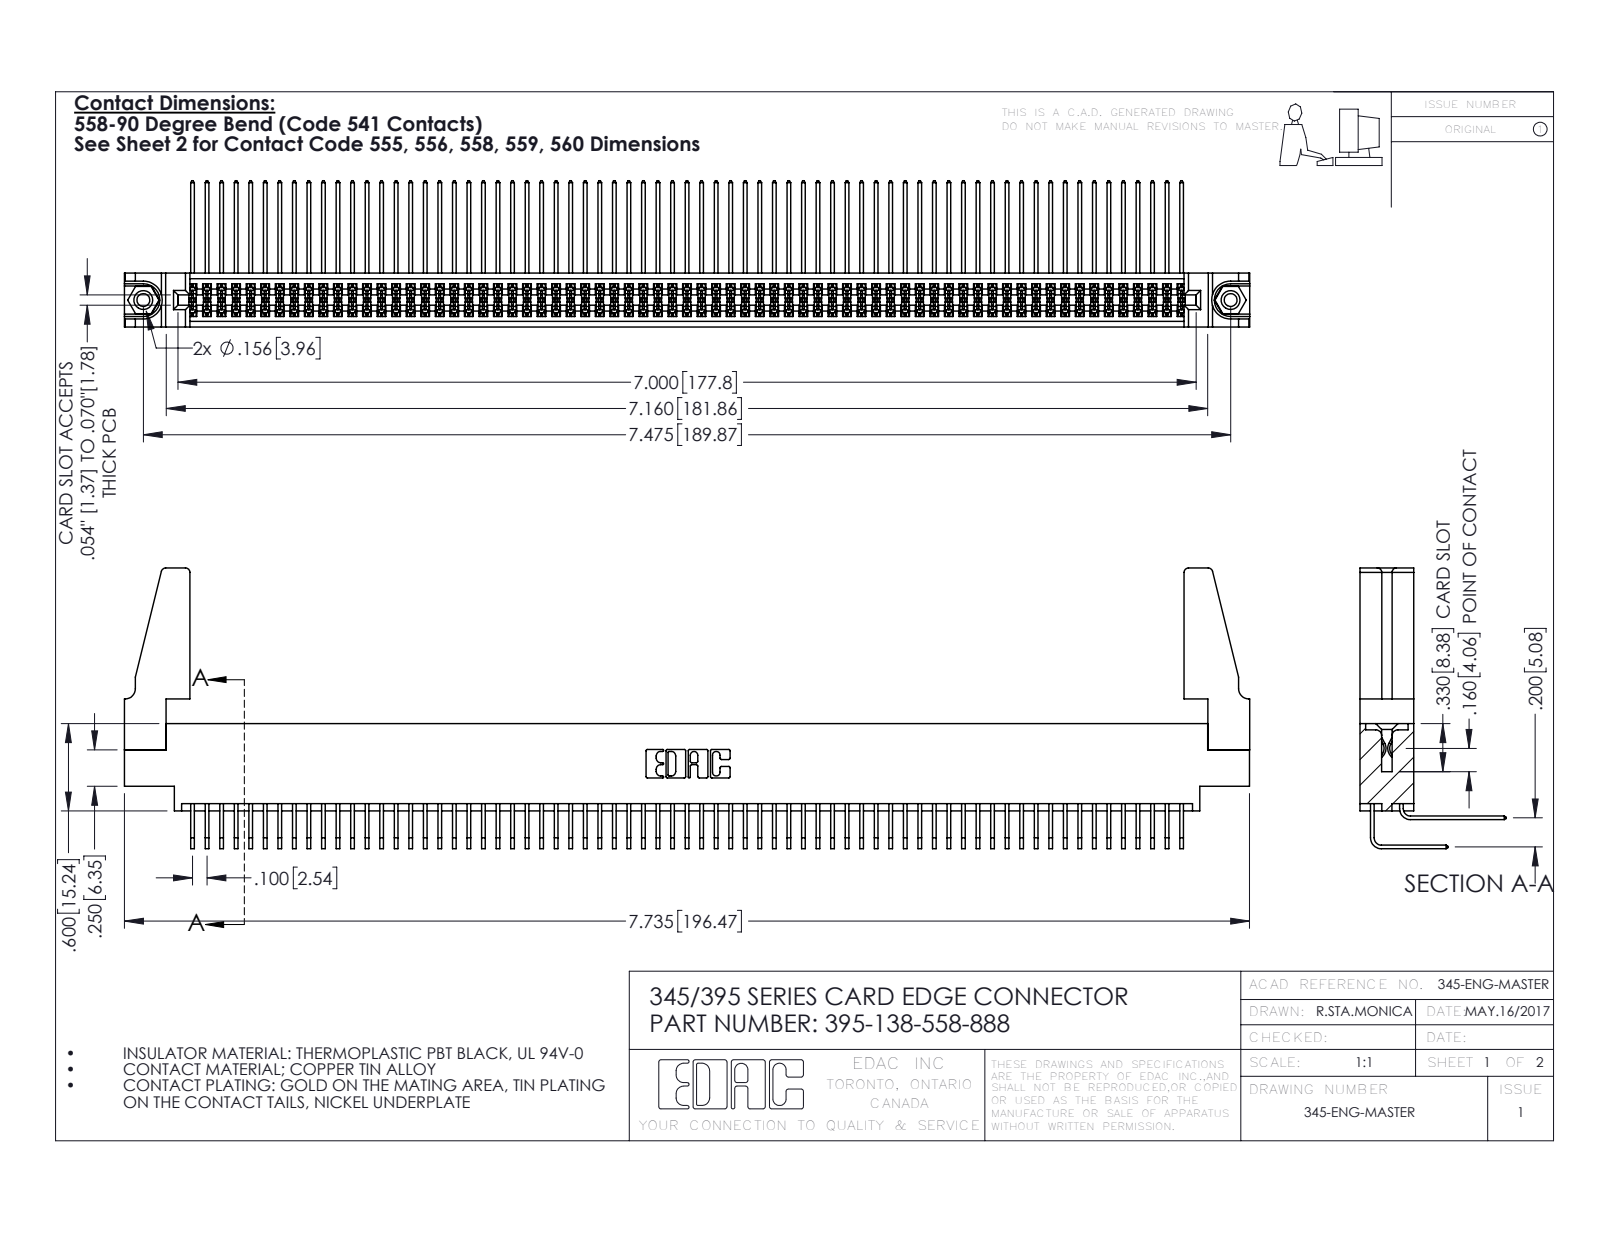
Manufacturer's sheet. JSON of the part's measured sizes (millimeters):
{"part_name": "345-292-001_558 Tail - 2; 395-138-558-888; 345-292-001_558 559 Tail - 1; 345-250-001_345-250-001-102 (+2 more)", "step_written_by": "SolidWorks 2016 (CONFIG_CONTROL_DESIGN)", "units": "millimeters", "bodies": {"solids": 143, "faces": 7430, "planar": 4986, "cylindrical": 2428, "other": 16}, "overall_size": [196.5, 49, 25.5], "volume_mm3": 23270, "surface_area_mm2": 37130, "round_holes": [[2.3, 2], [3.2, 2], [4, 2], [1.6, 1]], "round_bosses_or_shafts": [[3.9, 2]], "partial_cylinders_radius": [[0.2, 275], [0.3, 22], [0.8, 8], [0.2, 6], [0.8, 6], [0.7, 3], [0.4, 2], [0.5, 2]], "face_to_face_distances": [1.8, 7.6, 5.1, 9.4, 2.5, 6.9, 0.6, 5.7, 4.4, 0.6], "hole_center_spacings": [6.9, 183.9, 189.9]}
